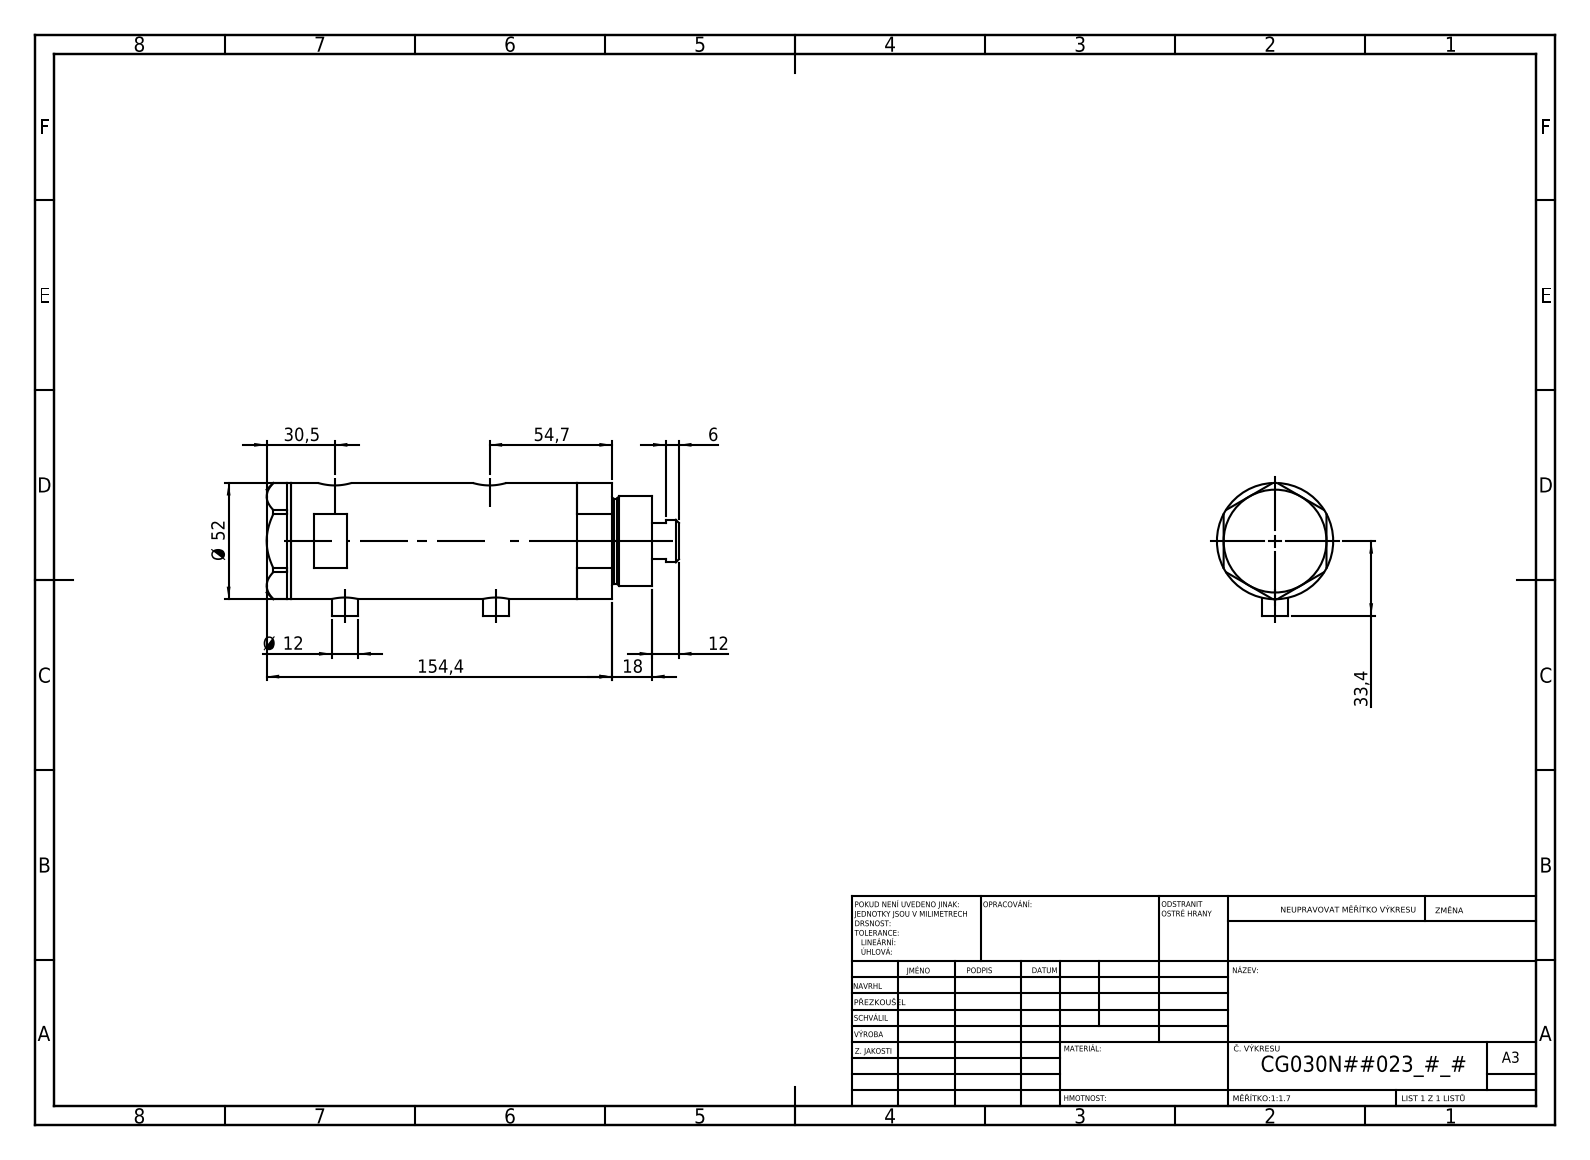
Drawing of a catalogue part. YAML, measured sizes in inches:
part_name: "V270CG_VC; V270CG_FRONT; V270CG_BACK; V270CG_MIDDLE"
step_written_by: "SolidWorks 2019 (CONFIG_CONTROL_DESIGN)"
units: inches
bodies: {solids: 4, faces: 134, planar: 65, cylindrical: 49, other: 20}
overall_size: [7.26, 2.339, 2.047]
volume: 20.61
surface_area: 119.9
round_holes:
  - {diameter: 0.383, count: 2}
  - {diameter: 0.492, count: 2}
  - {diameter: 0.591, count: 2}
  - {diameter: 0.256, count: 1}
  - {diameter: 0.787, count: 1}
  - {diameter: 0.846, count: 1}
  - {diameter: 1.181, count: 1}
  - {diameter: 1.299, count: 1}
  - {diameter: 1.732, count: 1}
round_bosses_or_shafts:
  - {diameter: 0.472, count: 2}
  - {diameter: 2.047, count: 1}
  - {diameter: 1.575, count: 1}
  - {diameter: 1.496, count: 1}
  - {diameter: 0.748, count: 1}
face_to_face_distances: [3.602, 0.937, 2.665, 0.433, 1.37, 4.035, 1.811, 5.469, 5.035, 4.098]
hole_center_spacings: [0.114, 0.177, 2.547, 2.661, 2.724, 2.839]
